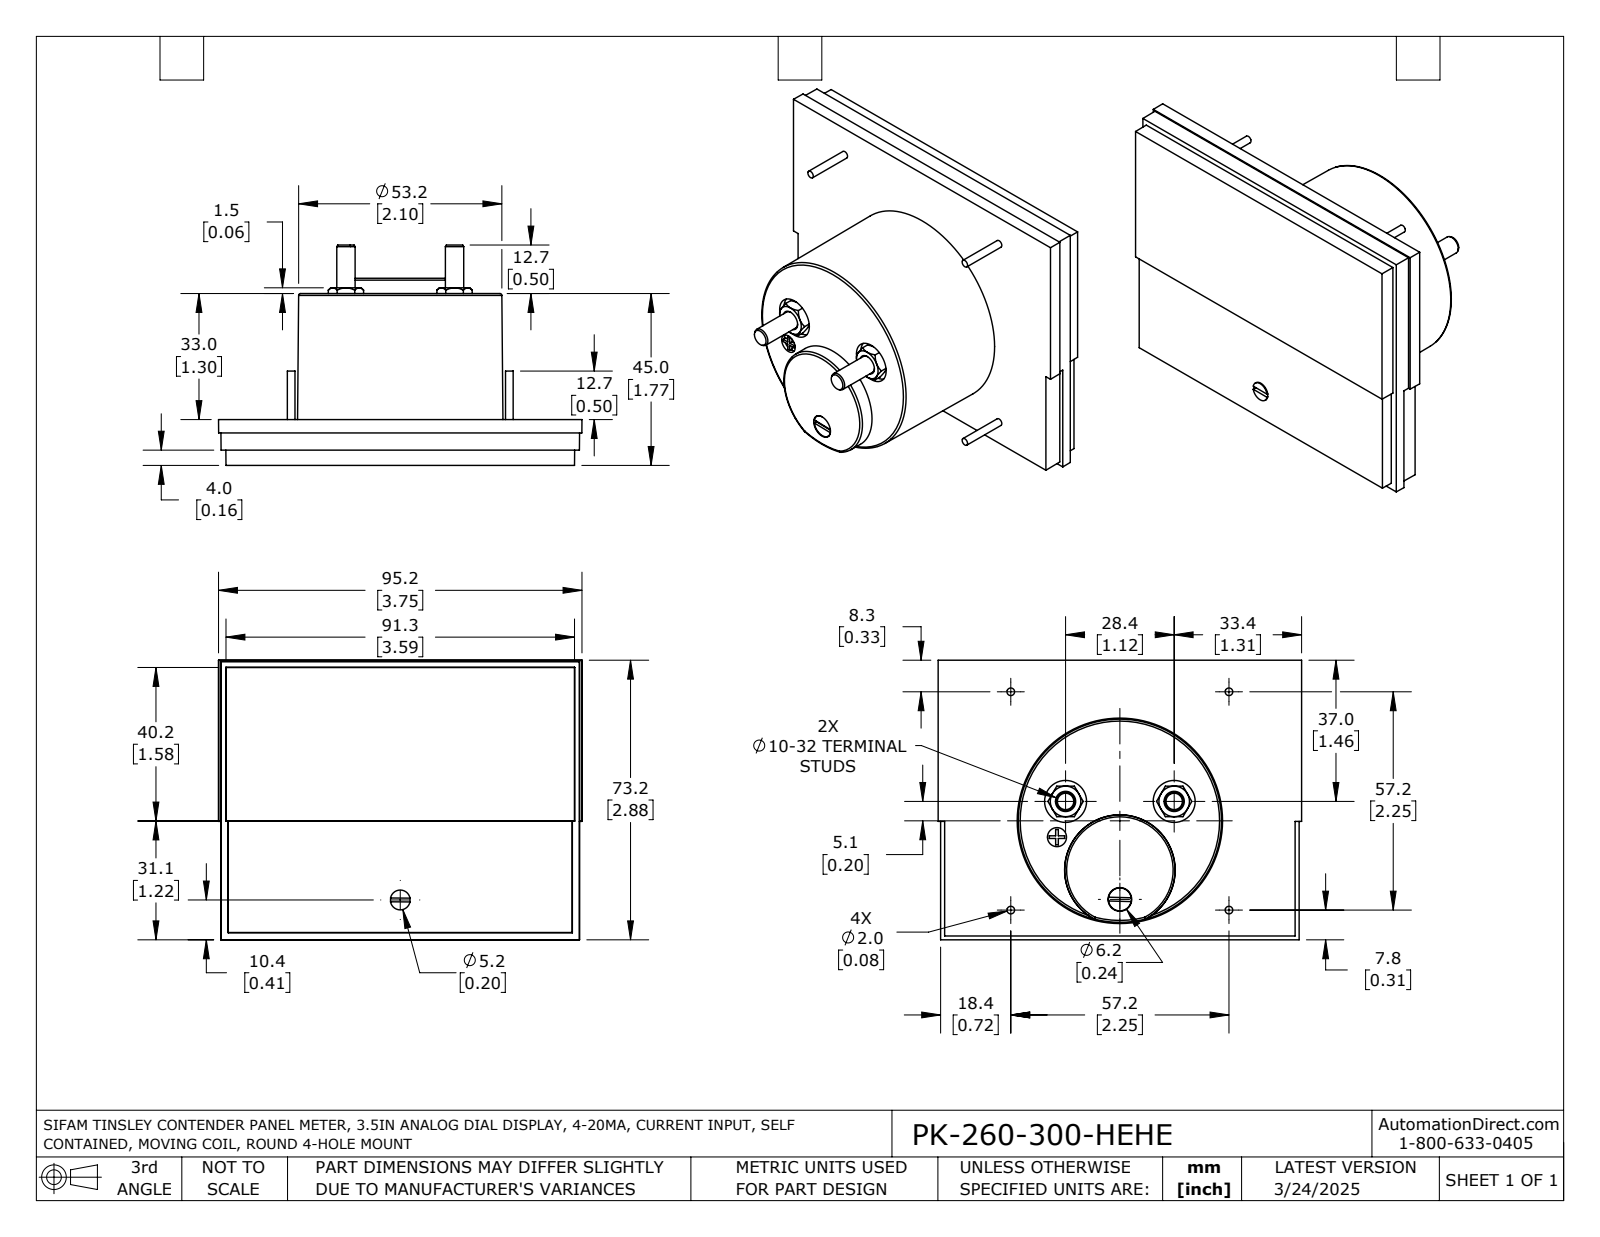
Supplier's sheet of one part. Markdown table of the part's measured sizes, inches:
| quantity | value |
| --- | --- |
| part name | PK-260-300-HEHE |
| STEP written by | SolidWorks 2021 (AUTOMOTIVE_DESIGN) |
| units | inches |
| bodies | 1 solid, 163 faces (76 planar, 31 cylindrical, 56 other) |
| overall size | 3.748 × 2.882 × 2.272 |
| volume | 9.446 in³ |
| surface area | 38.39 in² |
| round holes (diameter × count) | 0.433 × 2, 0.197 × 1, 0.244 × 1 |
| round bosses / shafts (diameter × count) | 0.079 × 4, 0.189 × 2, 0.236 × 1, 0.205 × 1 |
| partial cylindrical surfaces (radius × count) | 0.1 × 1 |
| main face-to-face distances | 0.472, 0.03, 0.443, 1.772, 1.299, 1.742, 0.157, 0.073, 0.315, 1.457 |
| hole center spacings | 1.155, 0.379, 0.912, 1.12, 1.263 |
